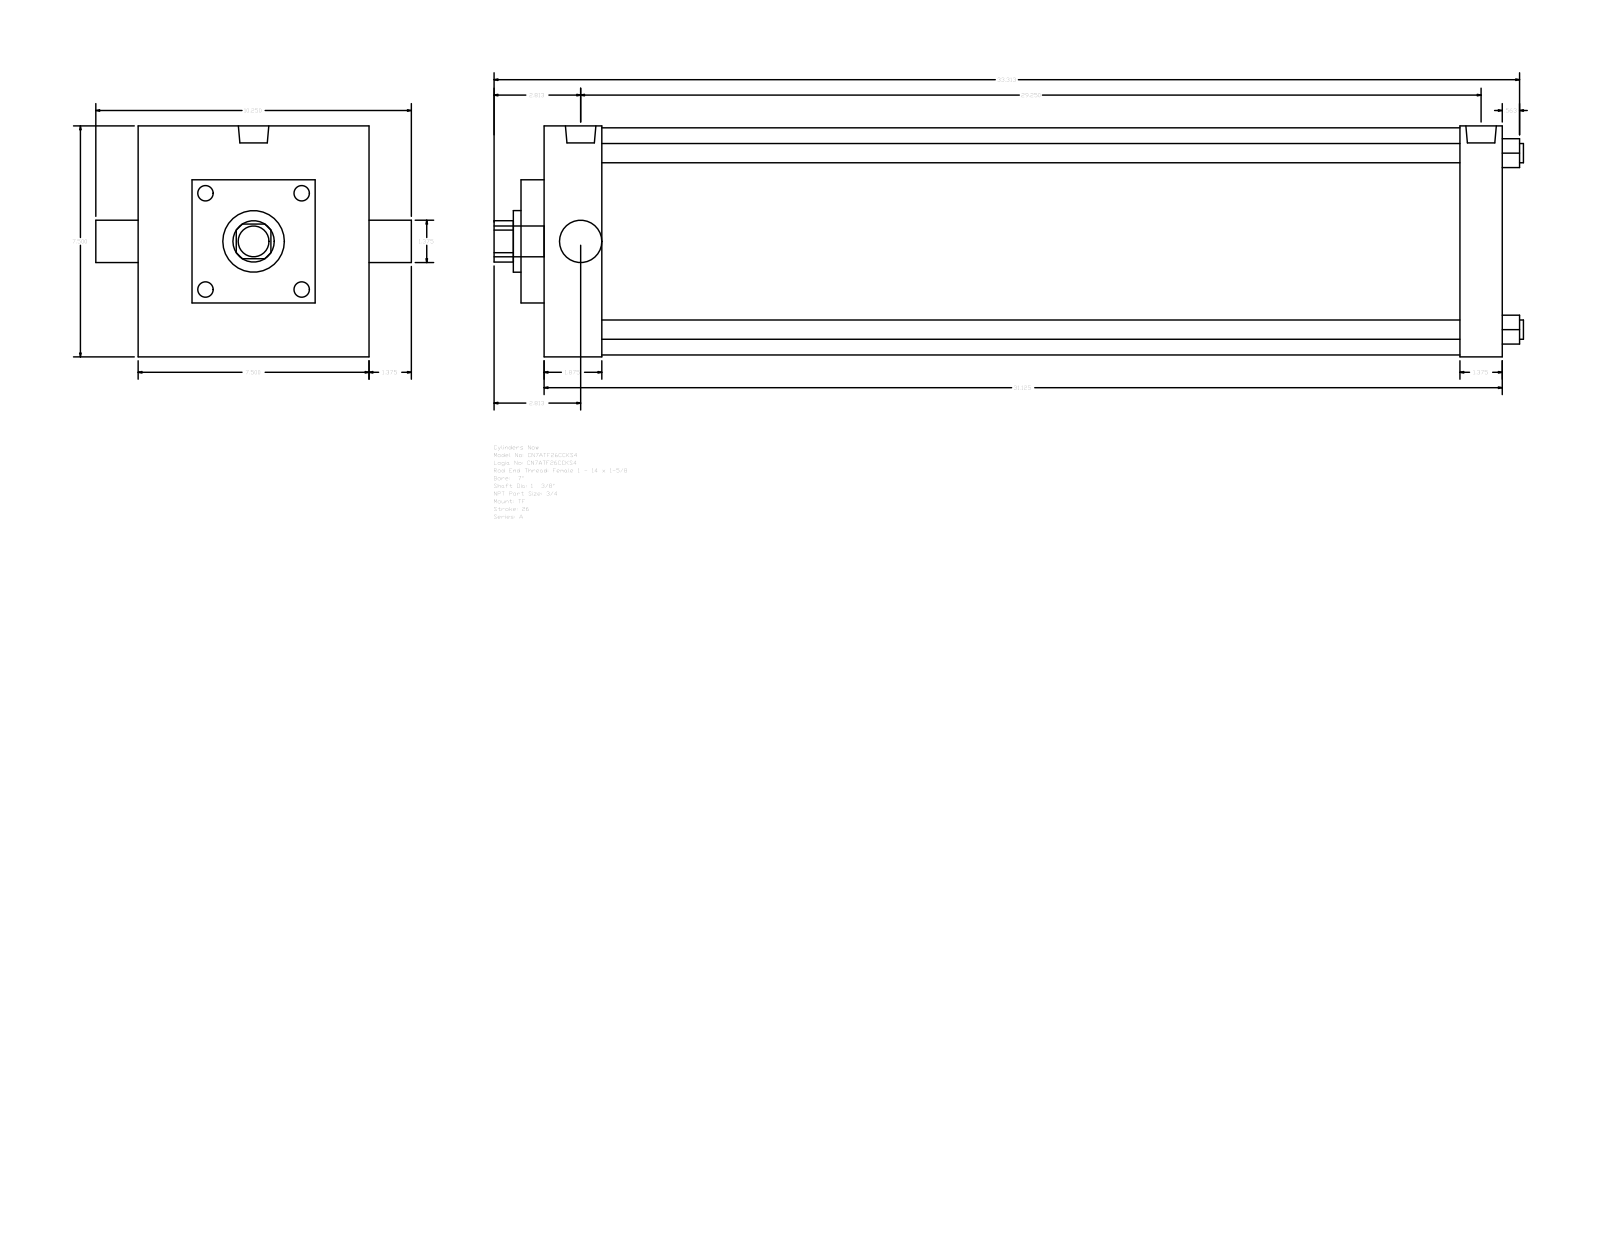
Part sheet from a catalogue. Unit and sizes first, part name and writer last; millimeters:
Units: millimetres
Overall size (bounding box): 849.31 × 260.35 × 190.5
Round holes (diameter × count): ⌀15.88 ×4, ⌀34.92 ×2, ⌀50.8 ×1, ⌀187.32 ×1
Round bosses / shafts (diameter × count): ⌀15.08 ×3, ⌀25.12 ×2, ⌀25.4 ×1
Partial cylindrical surfaces — rounded edges, fillets, slot ends (radius × count): R17.06 ×1
Main face-to-face distances: 190.5, 790.58, 34.93, 19.04, 809.62, 66.67, 47.63, 742.95, 774.69, 755.65
Hole centre spacings: 102.91, 145.54, 205.82
Bodies: 0 solids, 89 faces (65 planar, 24 cylindrical, 0 other)
Part name (STEP PRODUCT): A_TF__0700_1.375
STEP written by: GSSL Pune (CONFIG_CONTROL_DESIGN)
